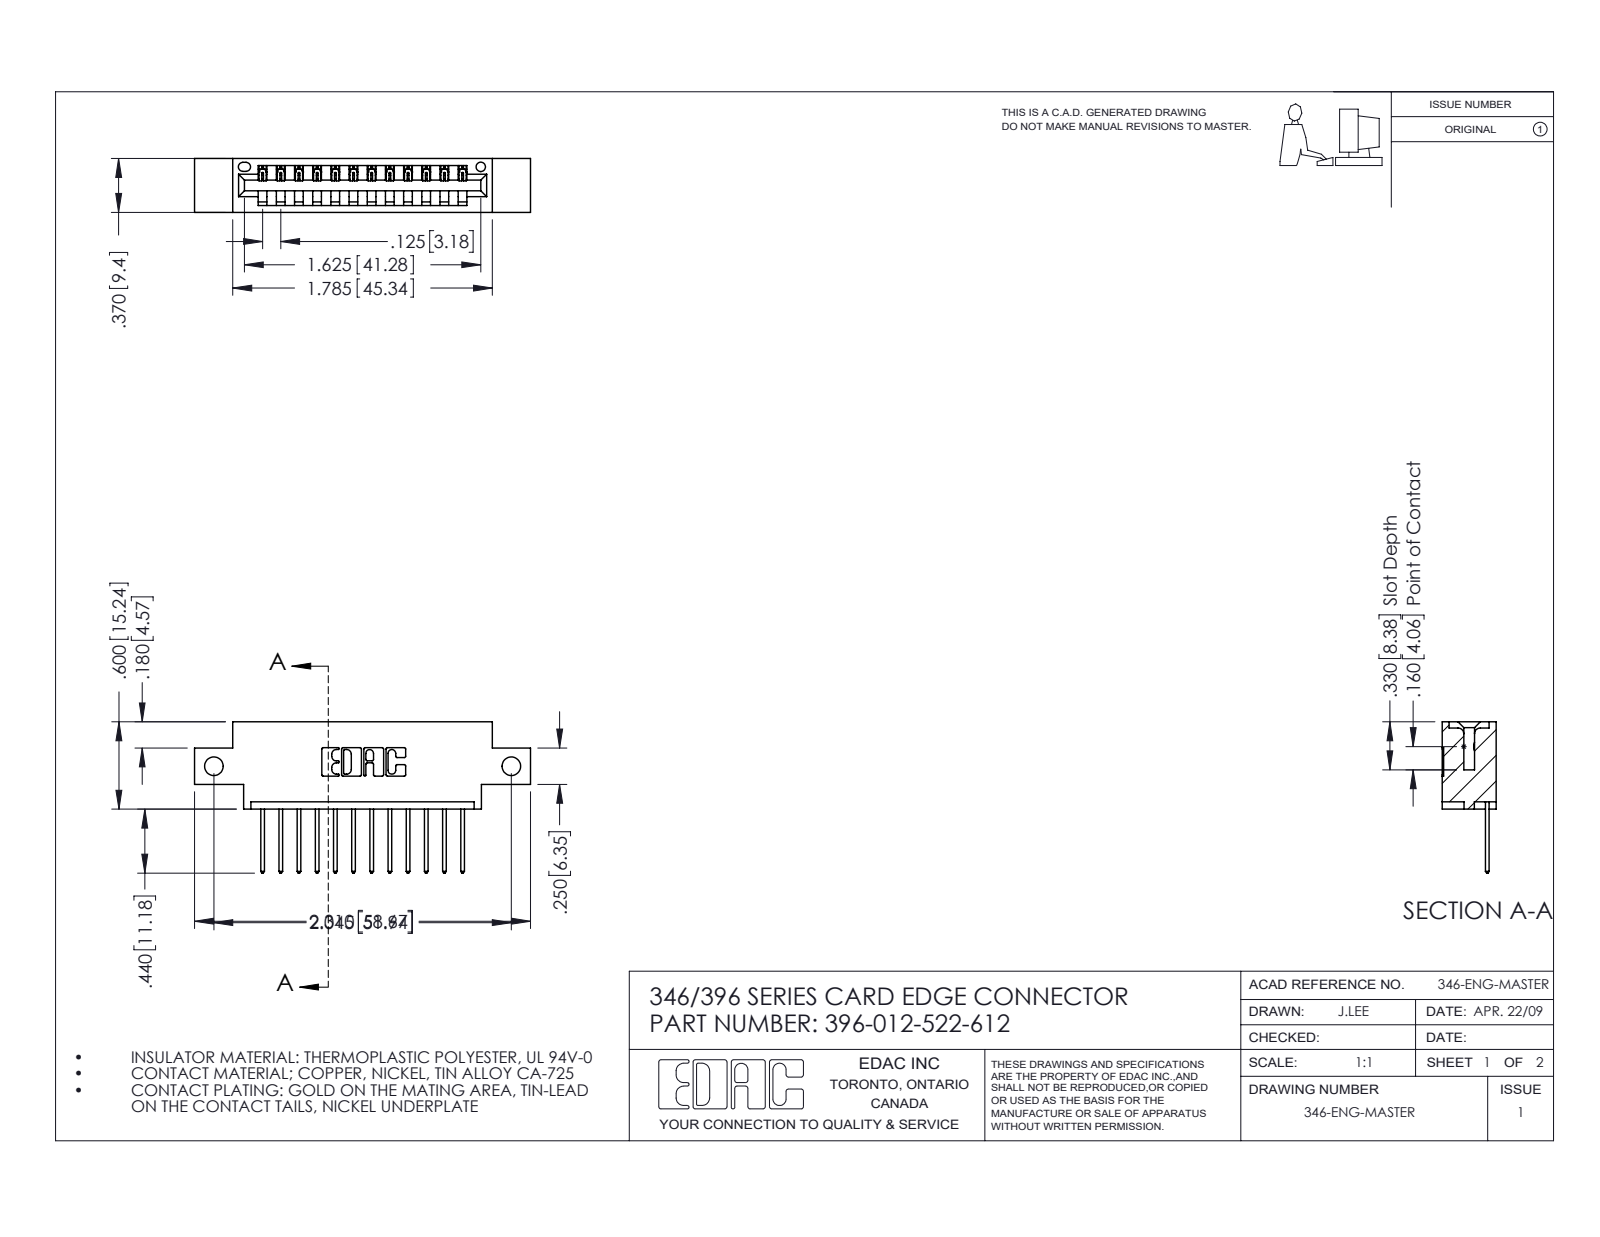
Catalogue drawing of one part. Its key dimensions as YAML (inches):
part_name: "346 Part_0.170 Offset - Side Mount; 396-012-522-612; 345-292-001_345-293-122"
step_written_by: "SolidWorks 2016 (CONFIG_CONTROL_DESIGN)"
units: inches
bodies: {solids: 13, faces: 822, planar: 560, cylindrical: 262, other: 0}
overall_size: [2.31, 1.04, 0.37]
volume: 0.315
surface_area: 9.604
round_holes:
  - {diameter: 0.128, count: 2}
  - {diameter: 0.064, count: 1}
partial_cylinders:
  - {radius: 0.006, count: 24}
  - {radius: 0.01, count: 24}
  - {radius: 0.01, count: 22}
  - {radius: 0.007, count: 6}
  - {radius: 0.031, count: 6}
  - {radius: 0.026, count: 3}
  - {radius: 0.031, count: 2}
  - {radius: 0.04, count: 2}
face_to_face_distances: [0.25, 0.37, 0.048, 0.322, 0.072, 0.298, 0.025, 0.148, 0.222, 0.1]
hole_center_spacings: [2.045]
